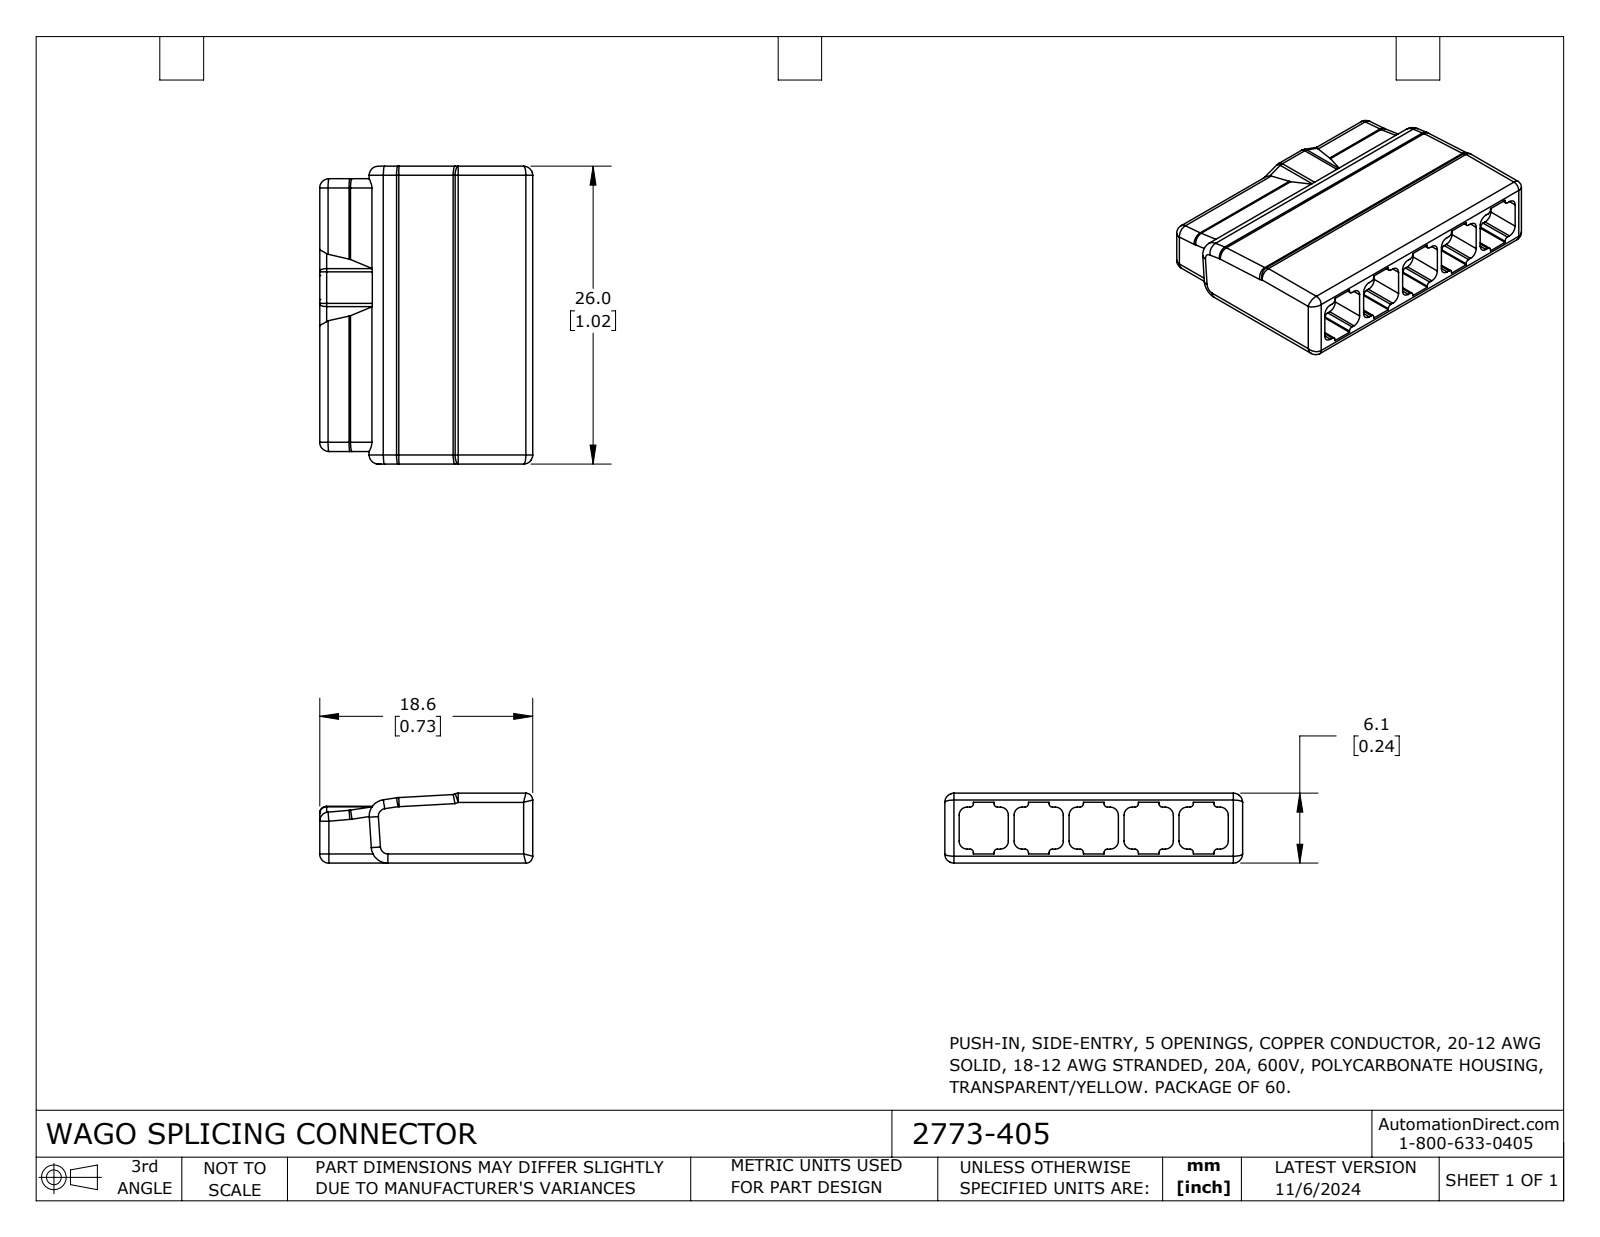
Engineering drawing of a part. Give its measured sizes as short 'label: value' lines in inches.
name: 2773-405
written by: SolidWorks 2023 (CONFIG_CONTROL_DESIGN)
unit: in
bodies: 1 solid, 190 faces (91 planar, 79 cylindrical, 20 other)
size: 1.024 × 0.732 × 0.24
volume: 0.145 in³; area: 2.534 in²
rounds: 27× R0.031, 20× R0.012, 20× R0.028, 5× R0.024, 2× R0.057, 2× R0.079
face distances: 0.24, 0.614, 0.189, 1.024, 0.209, 0.378, 0.031, 0.732, 0.118, 0.169
